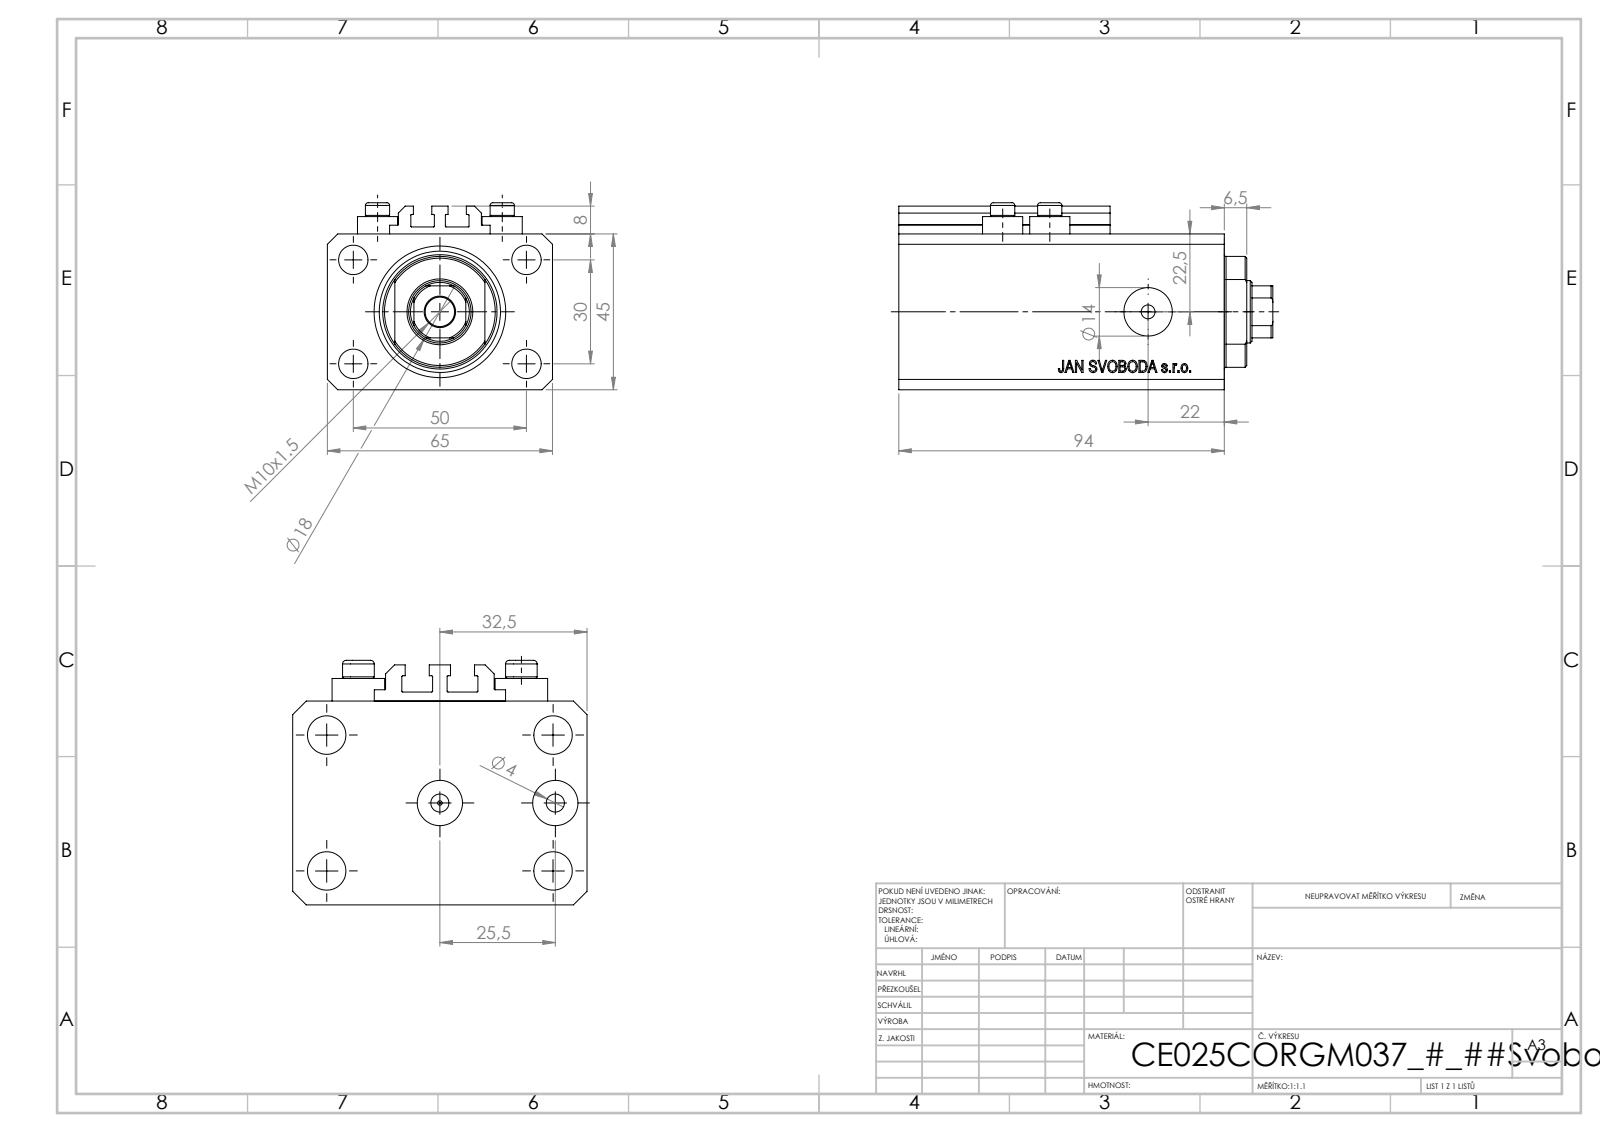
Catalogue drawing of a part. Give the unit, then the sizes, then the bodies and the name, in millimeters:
Units: millimetres
Overall size (bounding box): 108 × 65 × 54
Round holes (diameter × count): ⌀4 ×8, ⌀8.5 ×5, ⌀10 ×2, ⌀14 ×2, ⌀1.25 ×1, ⌀18 ×1, ⌀25 ×1, ⌀38 ×1
Round bosses / shafts (diameter × count): ⌀11.6 ×4, ⌀7 ×4
Partial cylindrical surfaces — rounded edges, fillets, slot ends (radius × count): R0.2 ×10, R8.5 ×1, R16 ×1
Main face-to-face distances: 45, 65, 14, 94, 80, 47, 6.9, 73.1, 87.1, 20.5
Hole centre spacings: 29.15, 50, 13.6, 15.01, 30, 36, 38.48, 52.68
Volume: 255 145 mm³ · Surface area: 67 191 mm²
Bodies: 8 solids, 1038 faces (504 planar, 88 cylindrical, 446 other)
Part name (STEP PRODUCT): V250CE_C_VCP; V250CE_VC_C; ALLEN BOLT V250CE; V250CE_C_Body
STEP written by: SolidWorks 2019 (CONFIG_CONTROL_DESIGN)
